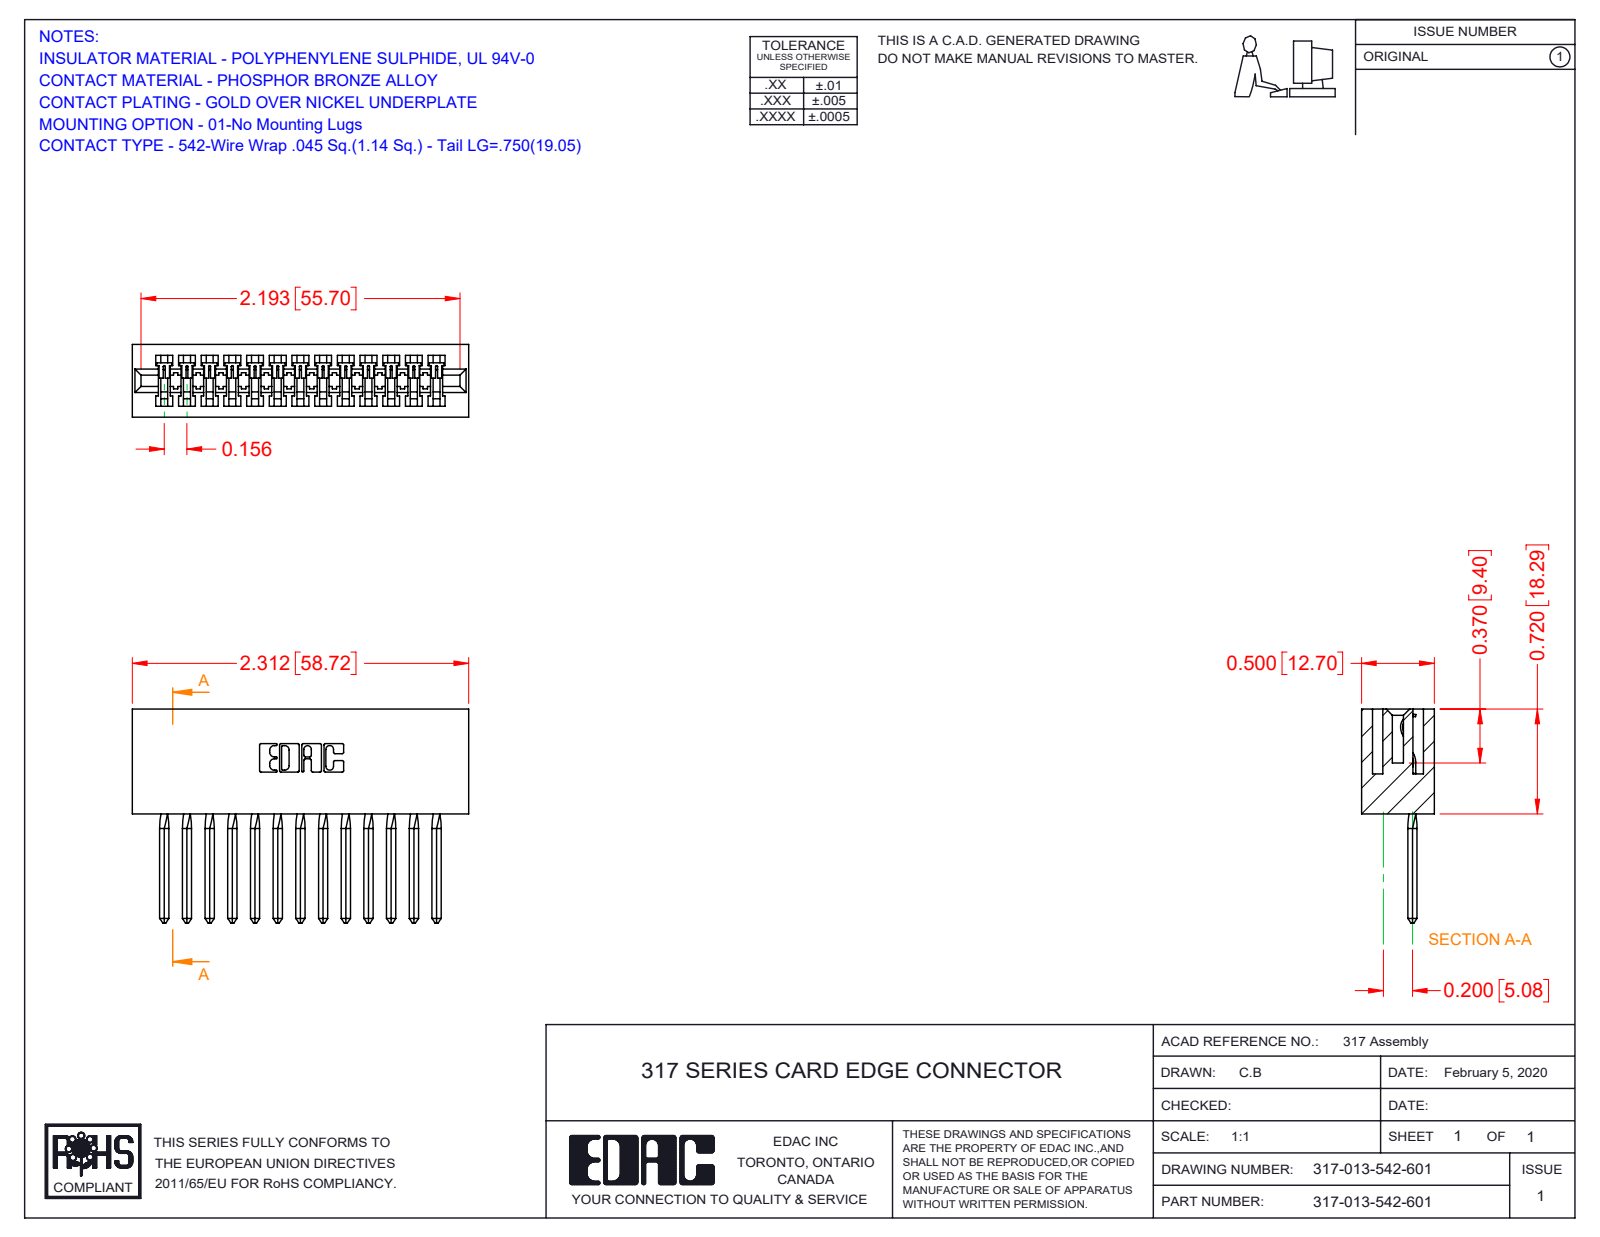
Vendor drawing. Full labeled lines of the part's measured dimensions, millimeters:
Part name (STEP PRODUCT): 317-013-542-601; 317-290-003_542; 317 Part_Lugless
STEP written by: SolidWorks 2016 (CONFIG_CONTROL_DESIGN)
Units: millimetres
Bodies: 14 solids, 1065 faces (882 planar, 131 cylindrical, 52 other)
Overall size (bounding box): 58.7 × 37.3 × 12.7
Volume: 9 880 mm³ · Surface area: 11 450 mm²
Partial cylindrical surfaces — rounded edges, fillets, slot ends (radius × count): R0.2 ×26, R0.3 ×22, R0.2 ×6, R0.8 ×6, R0.7 ×3, R1.9 ×1, R2.3 ×1, R2.5 ×1
Main face-to-face distances: 12.7, 1.9, 10.8, 2.8, 1.7, 8.9, 4, 5.6, 3.5, 2.9
